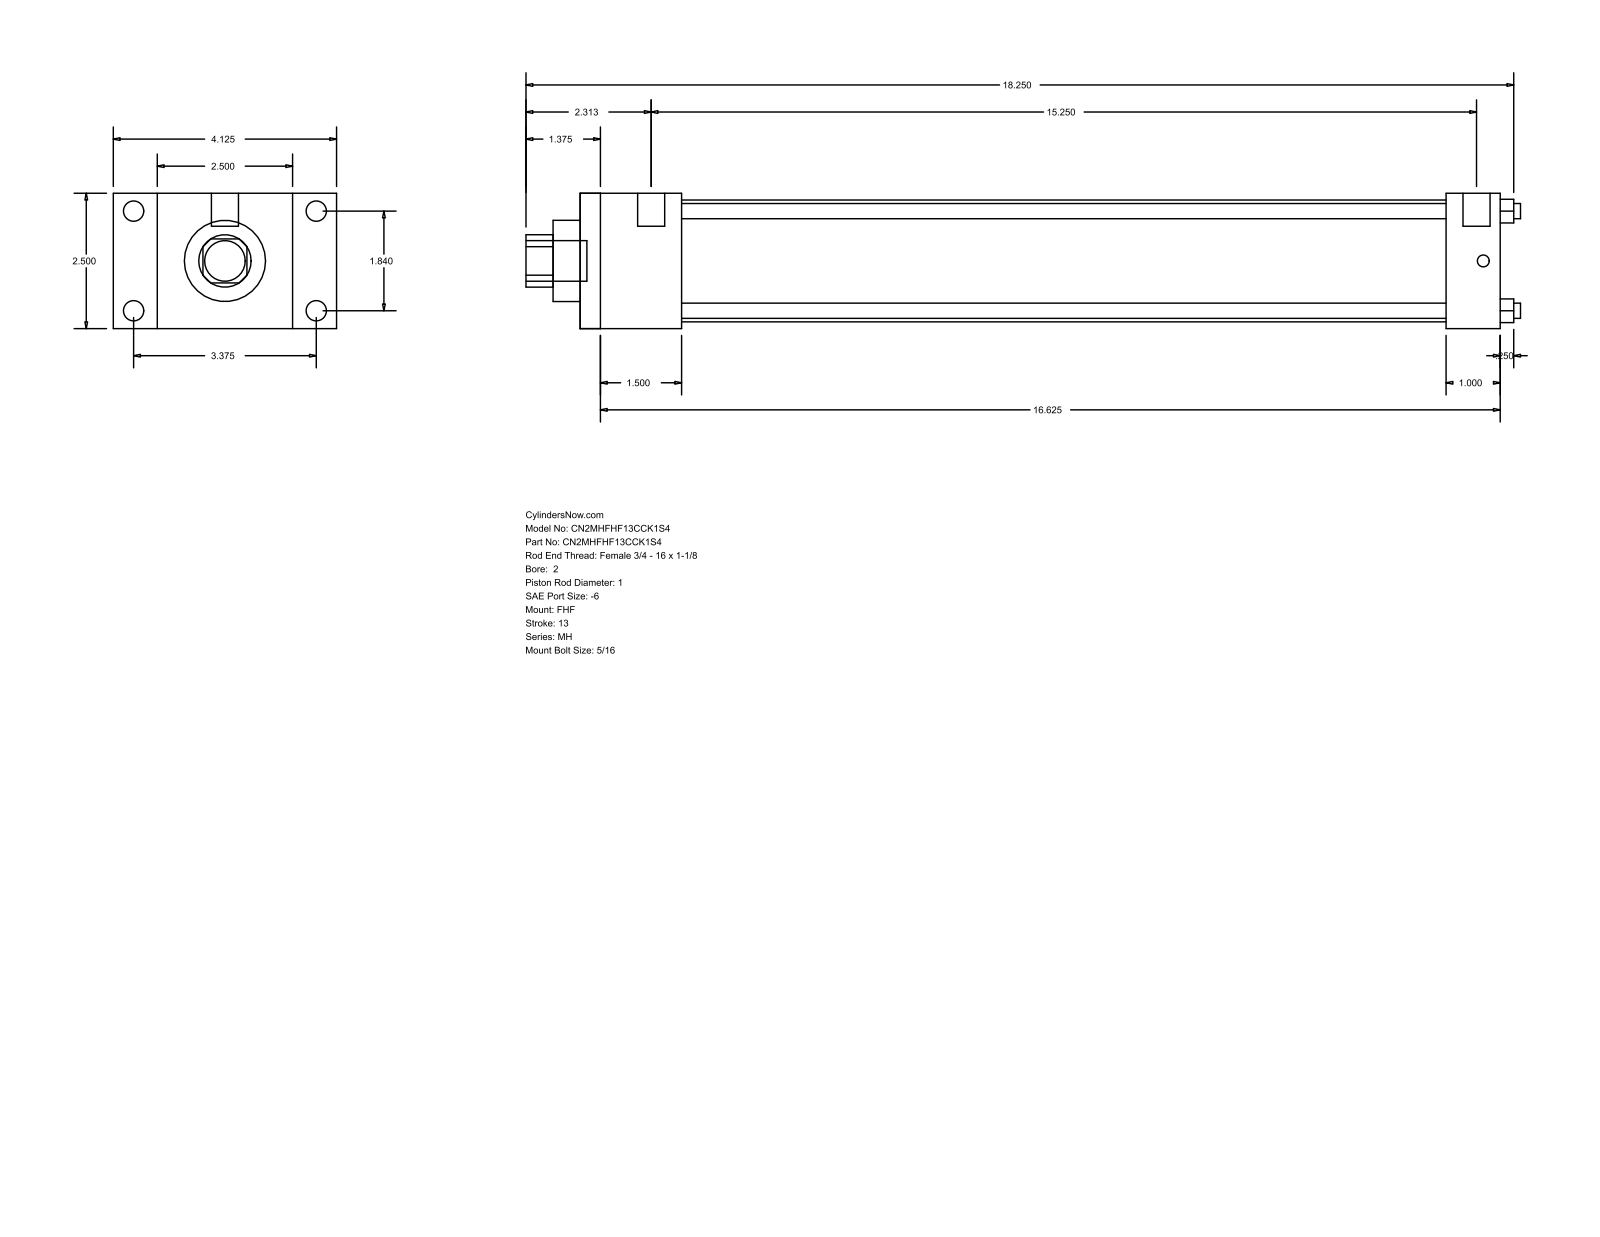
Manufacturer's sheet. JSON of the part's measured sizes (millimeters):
{"part_name": "MH_FHF__0200_1", "step_written_by": "GSSL Pune (CONFIG_CONTROL_DESIGN)", "units": "millimeters", "bodies": {"solids": 0, "faces": 88, "planar": 60, "cylindrical": 28, "other": 0}, "overall_size": [466.73, 104.78, 63.5], "round_holes": [[7.14, 4], [25.4, 1], [38.1, 1], [57.15, 1]], "round_bosses_or_shafts": [[9.53, 4], [5.56, 4], [12.7, 2], [19.05, 1]], "partial_cylinders_radius": [[12.29, 1]], "face_to_face_distances": [63.5, 431.8, 47.63, 384.17, 20.64, 84.14, 104.78, 25.4, 406.4, 358.77], "hole_center_spacings": [33.05, 46.74, 66.1]}
